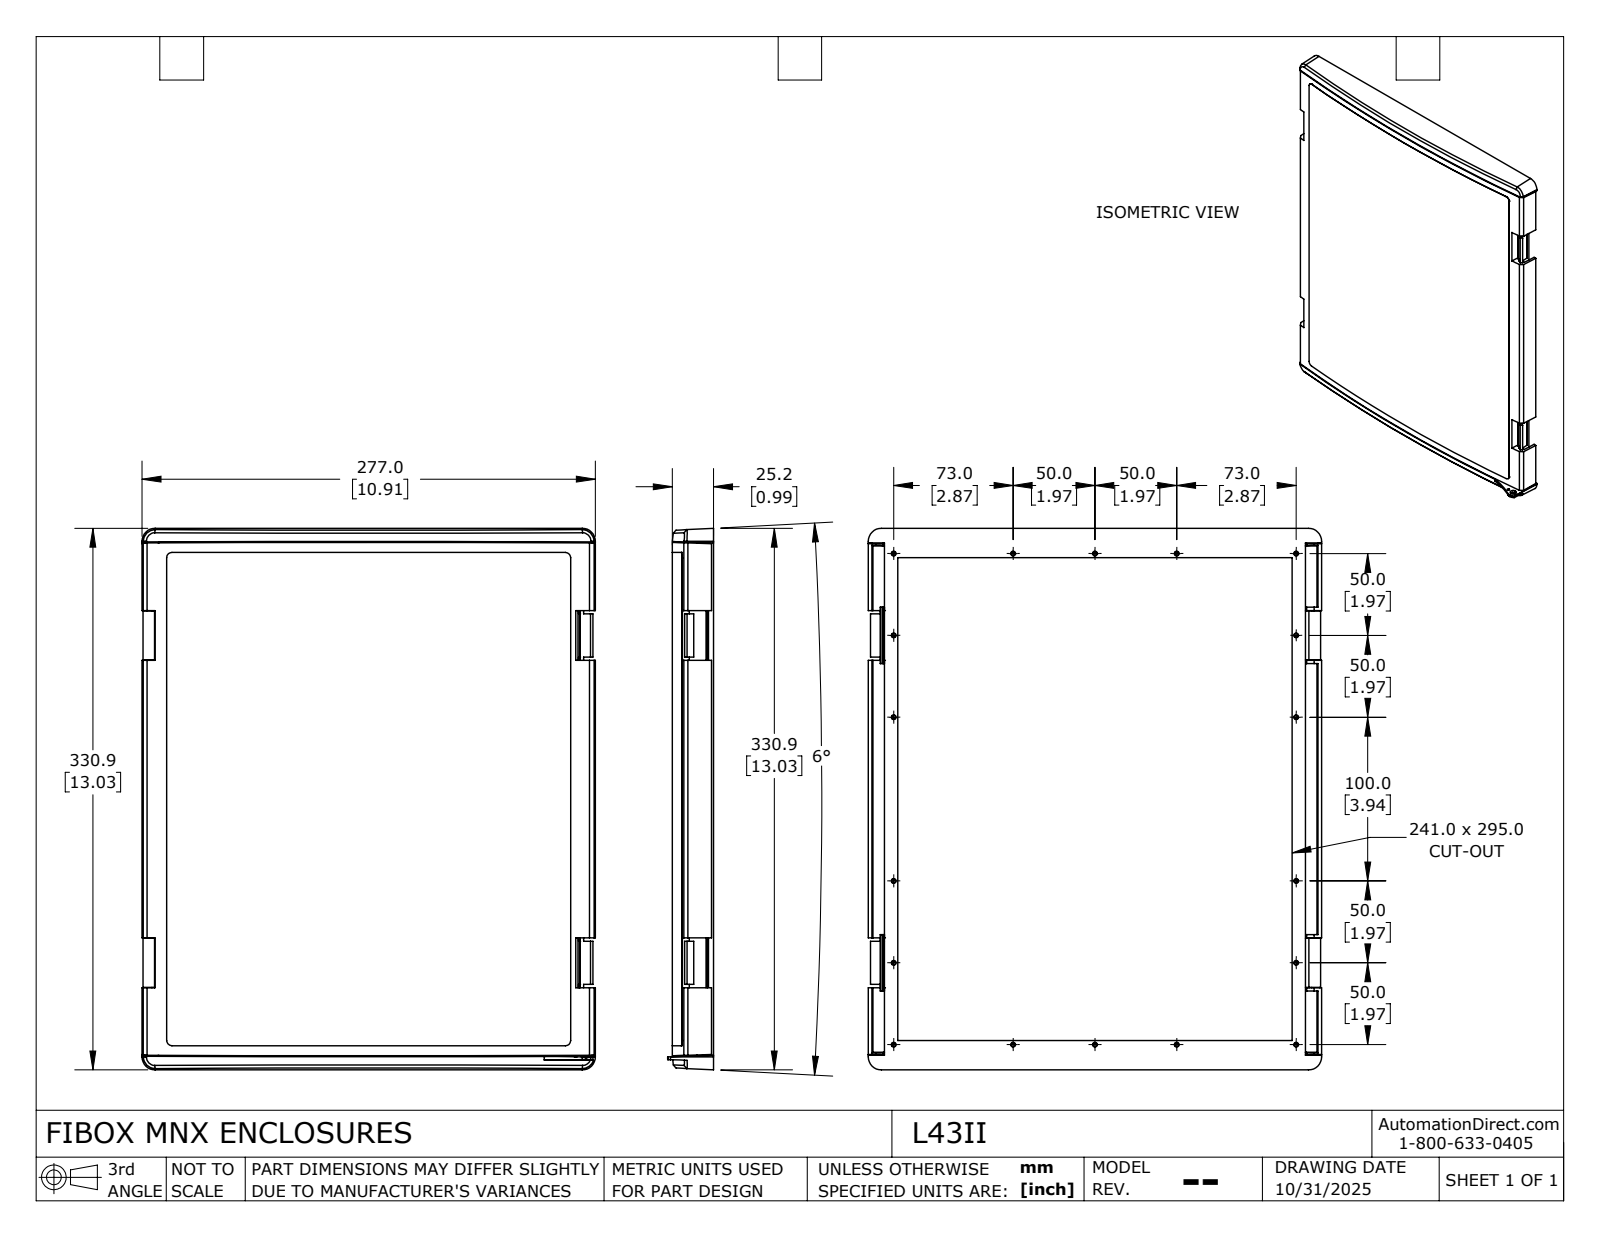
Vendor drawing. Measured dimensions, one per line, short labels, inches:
name: L43II_Default
written by: SolidWorks 2024 (CONFIG_CONTROL_DESIGN)
unit: in
bodies: 2 solids, 305 faces (179 planar, 96 cylindrical, 30 other)
size: 13.028 × 10.909 × 1.107
volume: 30.35 in³; area: 429.7 in²
holes: 18× ⌀0.087, 18× ⌀0.114
bosses: 1× ⌀0.197
rounds: 3× R0.177, 1× R0.039, 1× R0.102, 1× R51.083, 1× R51.181, 1× R51.182
face distances: 0.508, 0.512, 0.39, 0.023, 0.087, 0.304, 9.488, 12.098, 12.075, 11.614
hole spacings: 1.969, 3.937, 9.883, 7.874, 9.685, 10.455, 12.482, 11.811
